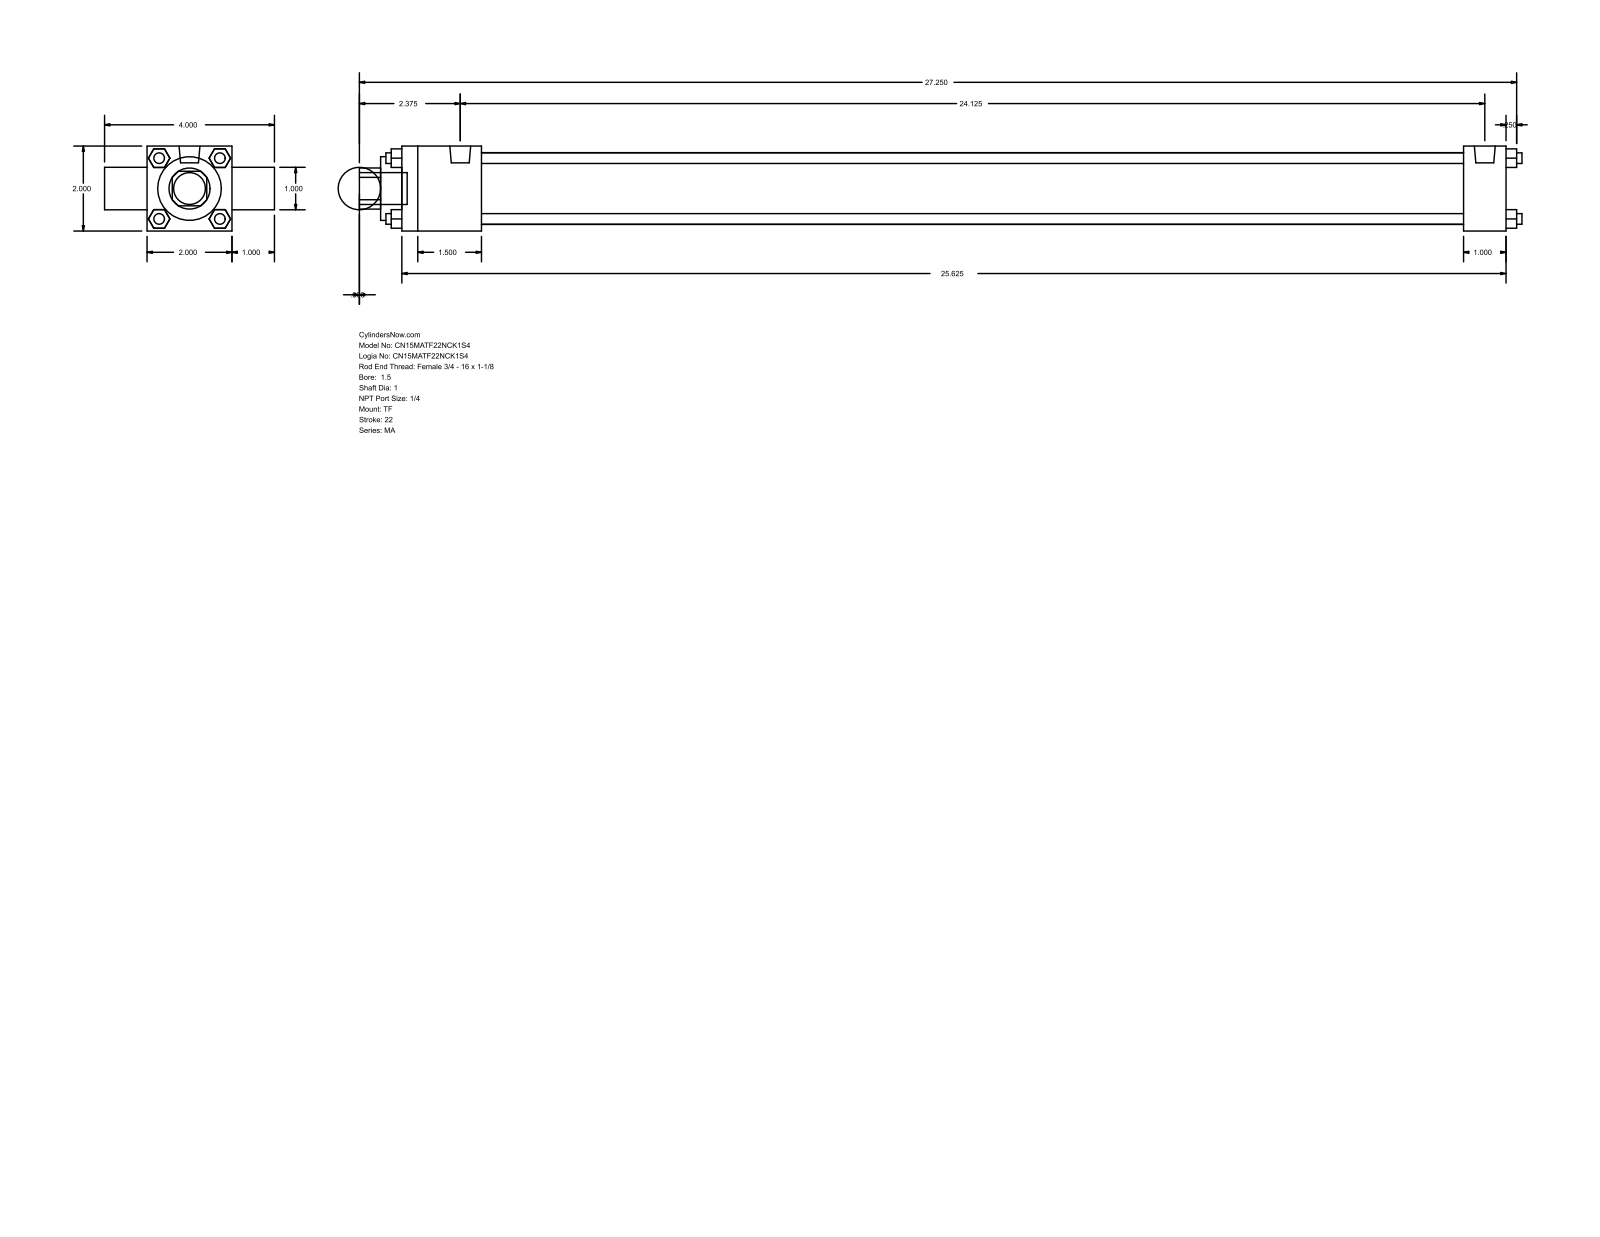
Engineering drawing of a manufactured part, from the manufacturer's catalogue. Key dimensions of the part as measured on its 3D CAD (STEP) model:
Part name (STEP PRODUCT): MA_TF__0150_1
STEP written by: GSSL Pune (CONFIG_CONTROL_DESIGN)
Units: millimetres
Bodies: 0 solids, 120 faces (92 planar, 28 cylindrical, 0 other)
Overall size (bounding box): 695.33 × 101.6 × 50.8
Round holes (diameter × count): ⌀25.4 ×2, ⌀38.1 ×1, ⌀42.93 ×1
Round bosses / shafts (diameter × count): ⌀6.35 ×4, ⌀7.94 ×3, ⌀12.49 ×2, ⌀19.05 ×1
Partial cylindrical surfaces — rounded edges, fillets, slot ends (radius × count): R12.29 ×1
Main face-to-face distances: 50.8, 25.4, 660.4, 76.2, 6.35, 47.63, 635, 587.37, 612.77, 673.1
